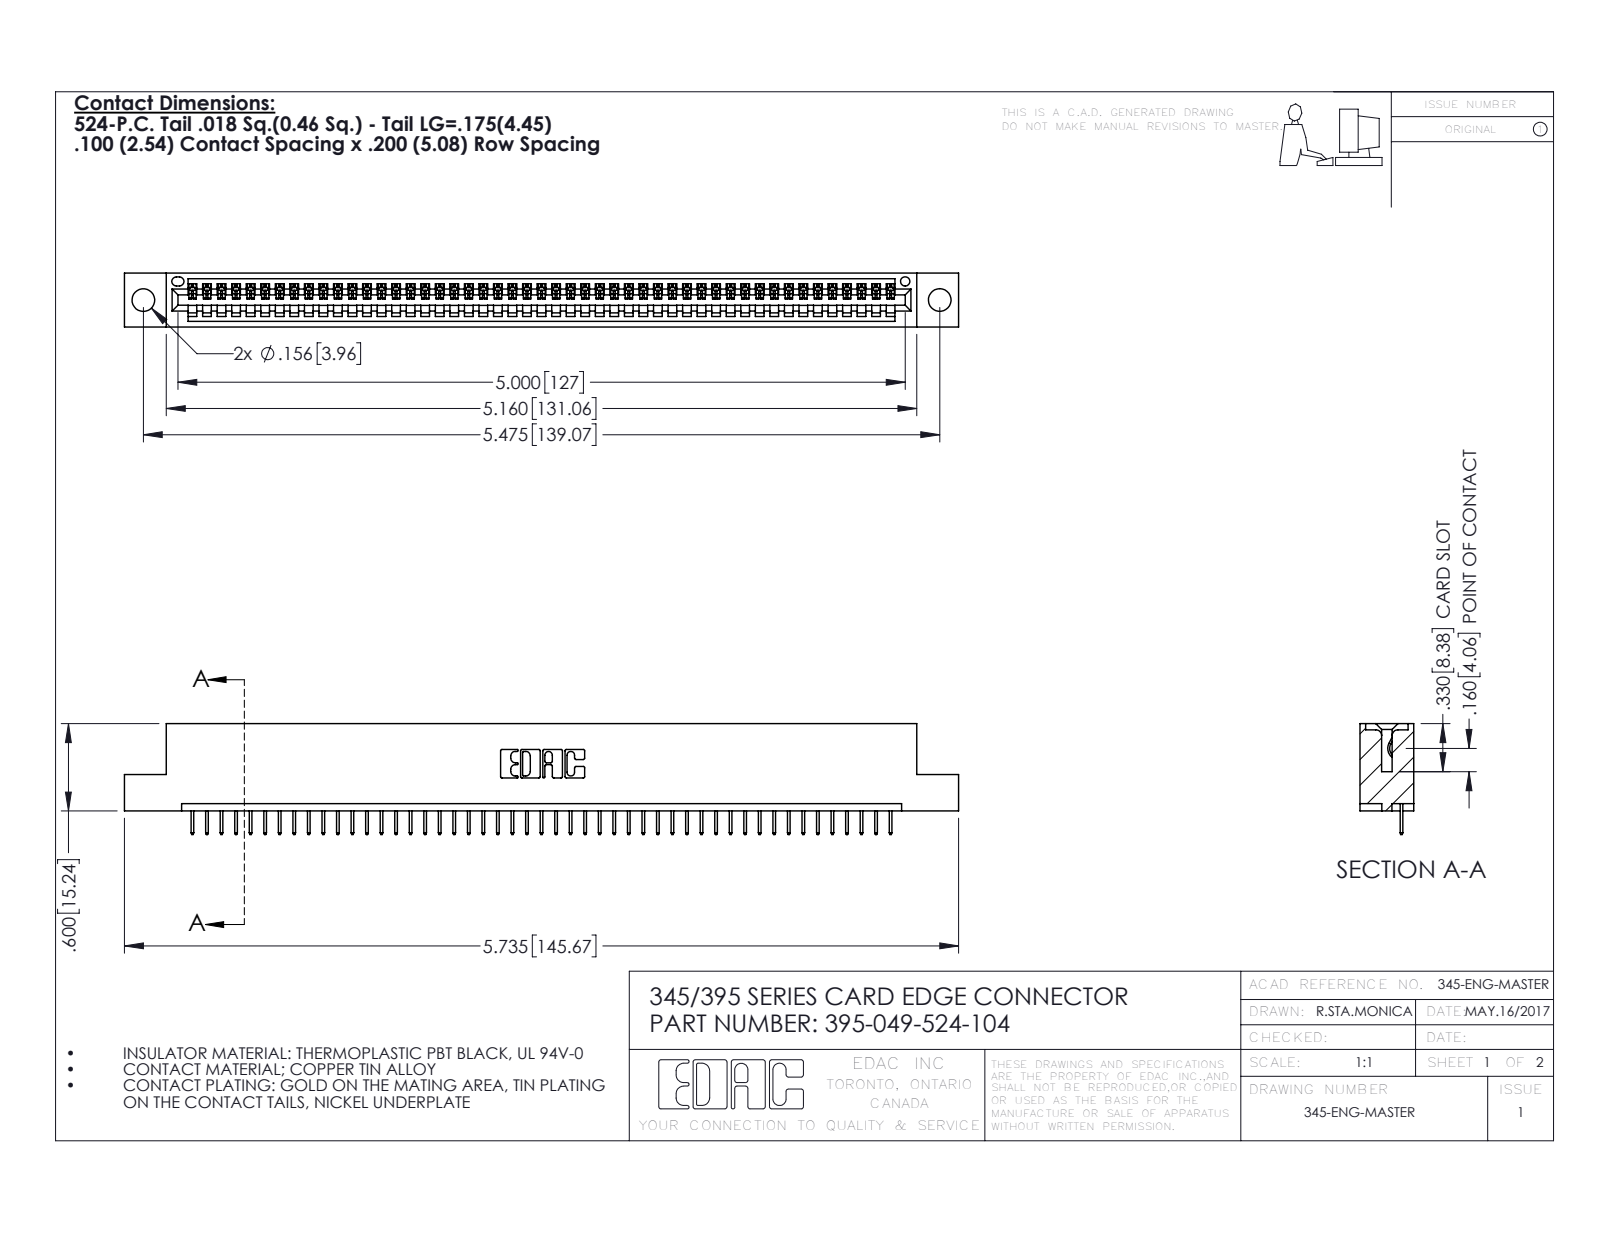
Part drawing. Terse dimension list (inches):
name: 345-292-001_345-293-124; 345 Part_Flush Mounting Lugs - 0.156 Dia-TH; 395-049-524-104
written by: SolidWorks 2016 (CONFIG_CONTROL_DESIGN)
unit: in
bodies: 50 solids, 3164 faces (2334 planar, 830 cylindrical, 0 other)
size: 5.735 × 0.762 × 0.37
volume: 0.831 in³; area: 26.93 in²
holes: 2× ⌀0.156, 1× ⌀0.064
rounds: 98× R0.006, 22× R0.01, 6× R0.007, 6× R0.031, 3× R0.026, 2× R0.031, 2× R0.04, 1× R0.014
face distances: 0.298, 0.072, 0.37, 0.2, 0.098, 0.272, 0.025, 0.225, 0.072, 0.149
hole spacings: 0.27, 5.239, 5.475
